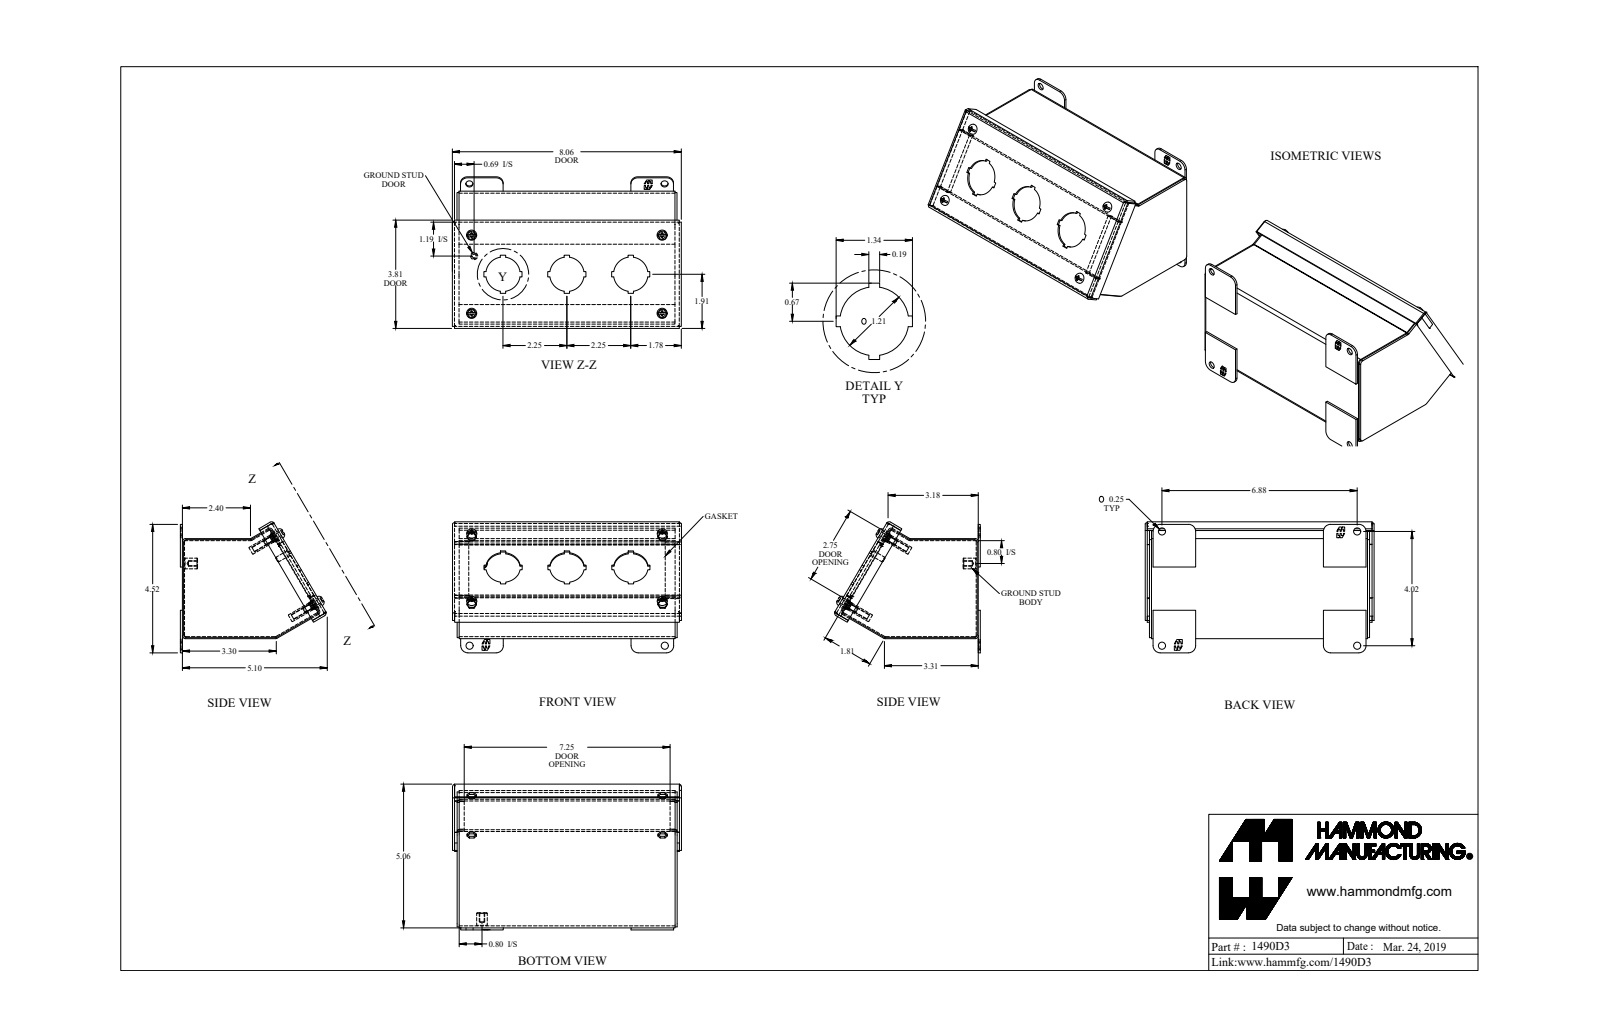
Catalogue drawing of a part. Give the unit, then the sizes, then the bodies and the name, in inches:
Units: inches
Overall size (bounding box): 8.062 × 5.133 × 4.613
Round holes (diameter × count): ⌀0.25 ×8, ⌀0.159 ×4, ⌀1.21 ×3, ⌀0.156 ×1
Round bosses / shafts (diameter × count): ⌀0.39 ×4, ⌀0.275 ×4, ⌀0.19 ×4, ⌀0.148 ×4, ⌀0.375 ×1, ⌀0.25 ×1, ⌀0.188 ×1
Partial cylindrical surfaces — rounded edges, fillets, slot ends (radius × count): R0.108 ×18, R0.036 ×12, R0.25 ×8, R0.125 ×4, R0.16 ×4, R0.171 ×4
Main face-to-face distances: 0.072, 3.45, 0.072, 7.678, 3.522, 3.378, 7.606, 7.75, 0.188, 3.428
Hole centre spacings: 6.71, 6.724, 1.764, 2.25, 2.75, 2.751, 2.756, 3.626
Volume: 15.37 in³ · Surface area: 403.4 in²
Bodies: 26 solids, 681 faces (481 planar, 160 cylindrical, 40 other)
Part name (STEP PRODUCT): 1490D3_Default
STEP written by: SolidWorks 2019 (CONFIG_CONTROL_DESIGN)
